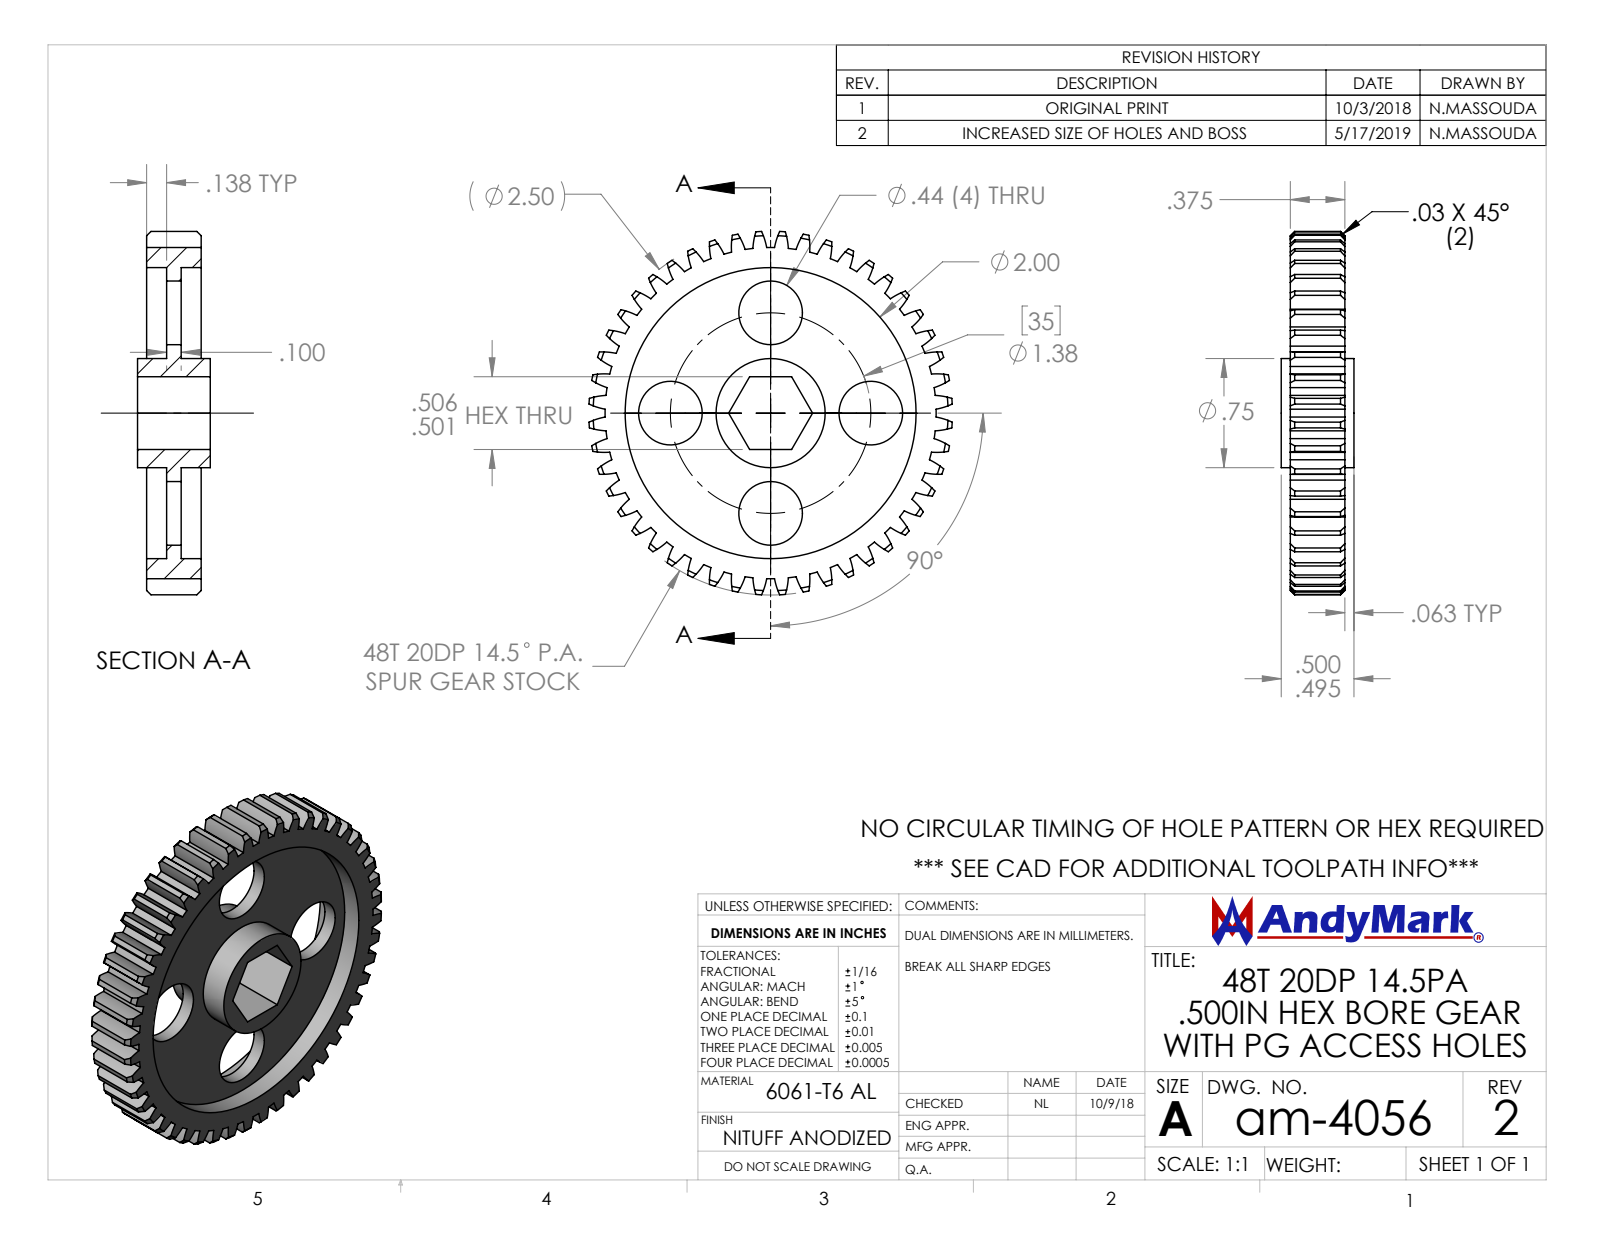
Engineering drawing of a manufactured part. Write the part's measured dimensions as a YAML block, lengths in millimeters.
part_name: "am-4056 48T 20DP 500hex 375 FW With Holes REV2"
step_written_by: "SolidWorks 2019 (CONFIG_CONTROL_DESIGN)"
units: millimeters
bodies: {solids: 1, faces: 321, planar: 12, cylindrical: 213, other: 96}
overall_size: [63.4, 63.4, 12.7]
volume: 13300
surface_area: 11030
round_holes:
  - {diameter: 11.1, count: 4}
  - {diameter: 50.8, count: 1}
round_bosses_or_shafts:
  - {diameter: 19.1, count: 1}
partial_cylinders:
  - {radius: 12.2, count: 96}
  - {radius: 28.9, count: 1}
  - {radius: 31.8, count: 1}
face_to_face_distances: [2.5, 3.5, 6, 9.5, 6, 3.5, 12.7, 5.1, 7.6, 11.1]
hole_center_spacings: [17.5, 24.7, 35]
